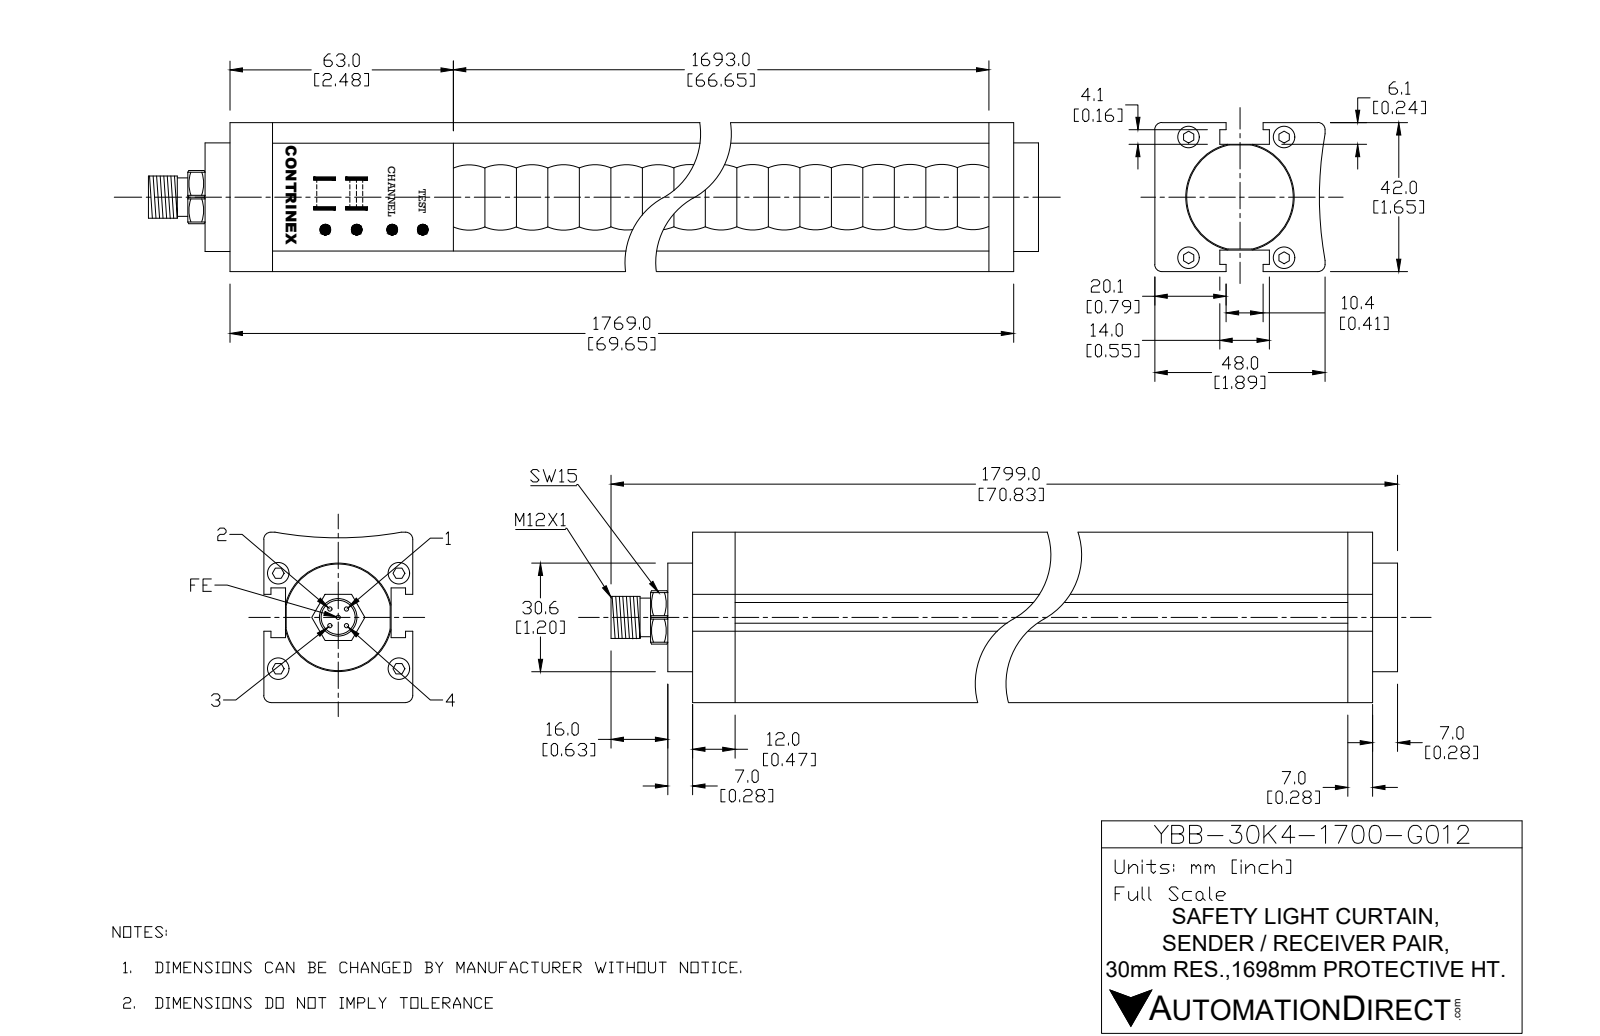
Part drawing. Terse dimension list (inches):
name: YBB-30K4-1700-G012
written by: SolidWorks 2019 (AUTOMOTIVE_DESIGN)
unit: in
bodies: 1 solid, 533 faces (121 planar, 152 cylindrical, 260 other)
size: 70.828 × 1.89 × 1.654
volume: 181.4 in³; area: 796.1 in²
holes: 4× ⌀0.12, 4× ⌀0.236, 1× ⌀0.335
bosses: 5× ⌀0.039, 4× ⌀0.217, 4× ⌀0.119, 1× ⌀1.205, 1× ⌀0.472, 1× ⌀0.413
rounds: 36× R0.035, 12× R0.039, 10× R0.016, 2× R0.217, 1× R0.02, 1× R0.02, 1× R0.323, 1× R0.689
face distances: 0.231, 1.422, 1.654, 1.191, 1.827, 2.172, 2.005, 0.2, 1.454, 0.031
hole spacings: 0.828, 0.88, 1.059, 1.339, 1.707
